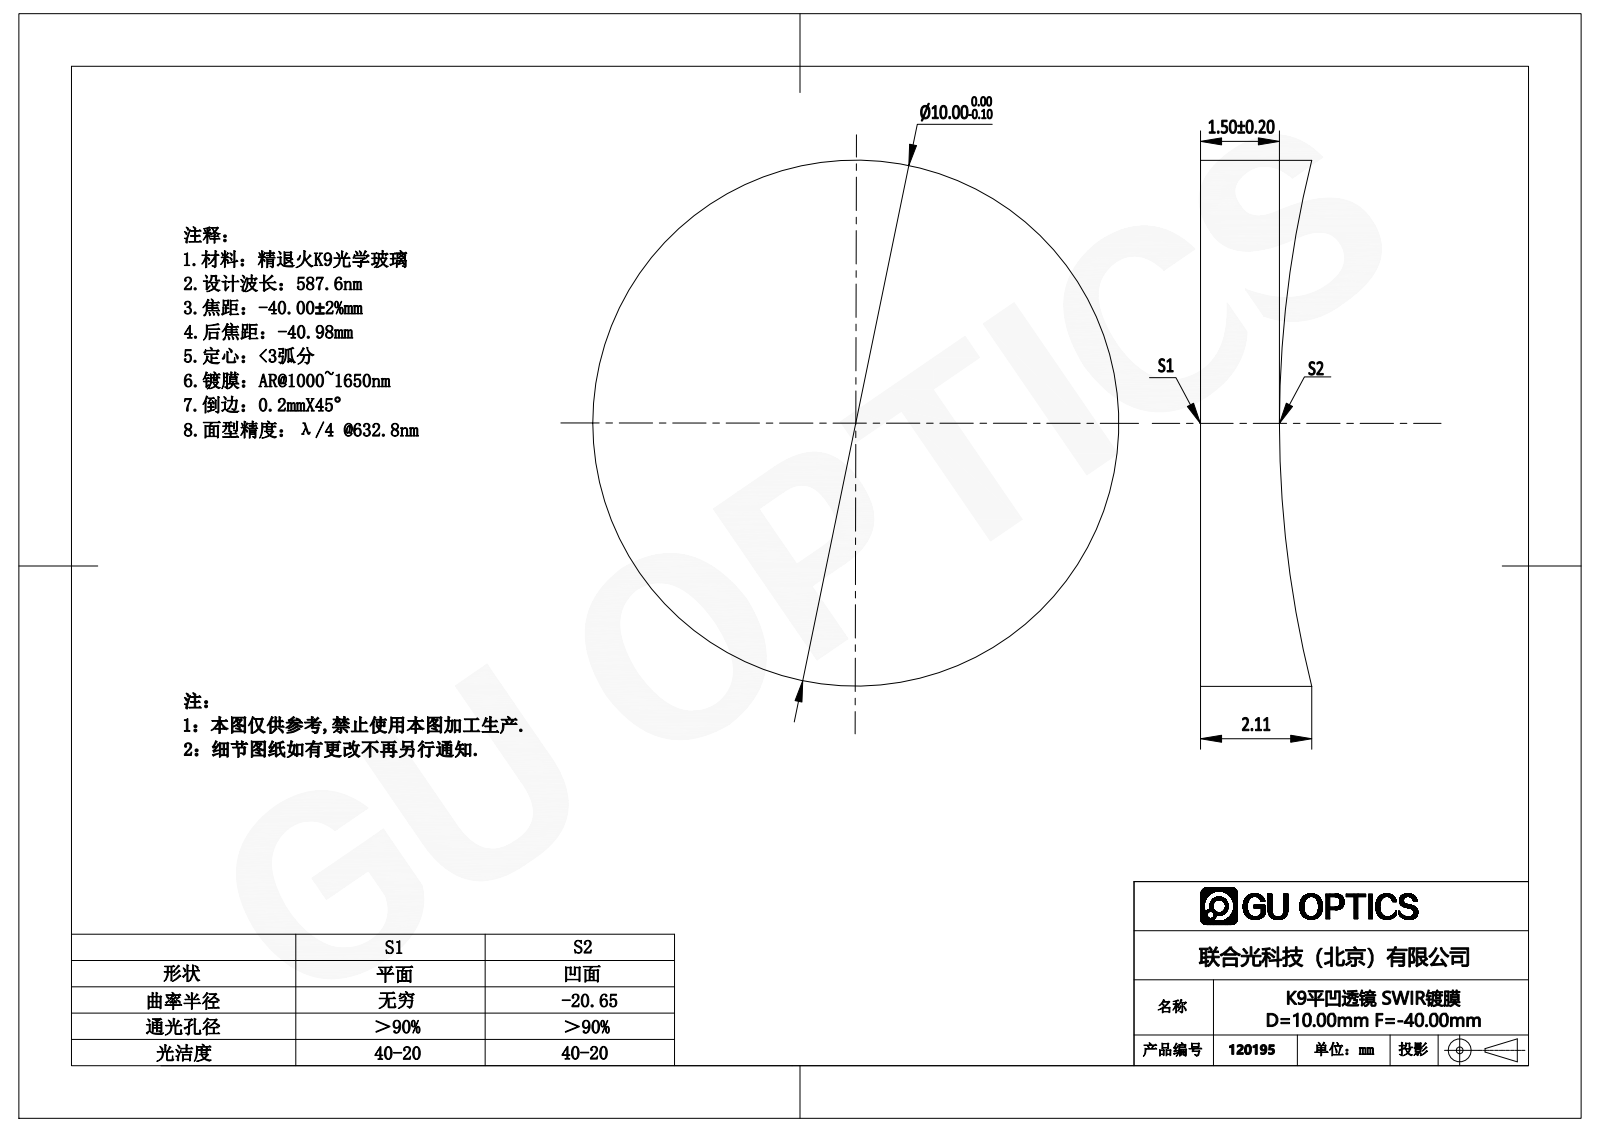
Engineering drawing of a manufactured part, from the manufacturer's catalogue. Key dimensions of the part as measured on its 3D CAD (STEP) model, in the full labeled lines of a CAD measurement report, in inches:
Part name (STEP PRODUCT): 120135
STEP written by: SolidWorks 2016 (AUTOMOTIVE_DESIGN)
Units: inches
Bodies: 1 solid, 5 faces (1 planar, 2 cylindrical, 2 other)
Overall size (bounding box): 0.394 × 0.394 × 0.083
Volume: 0.009 in³ · Surface area: 0.349 in²
Round bosses / shafts (diameter × count): ⌀0.394 ×1
